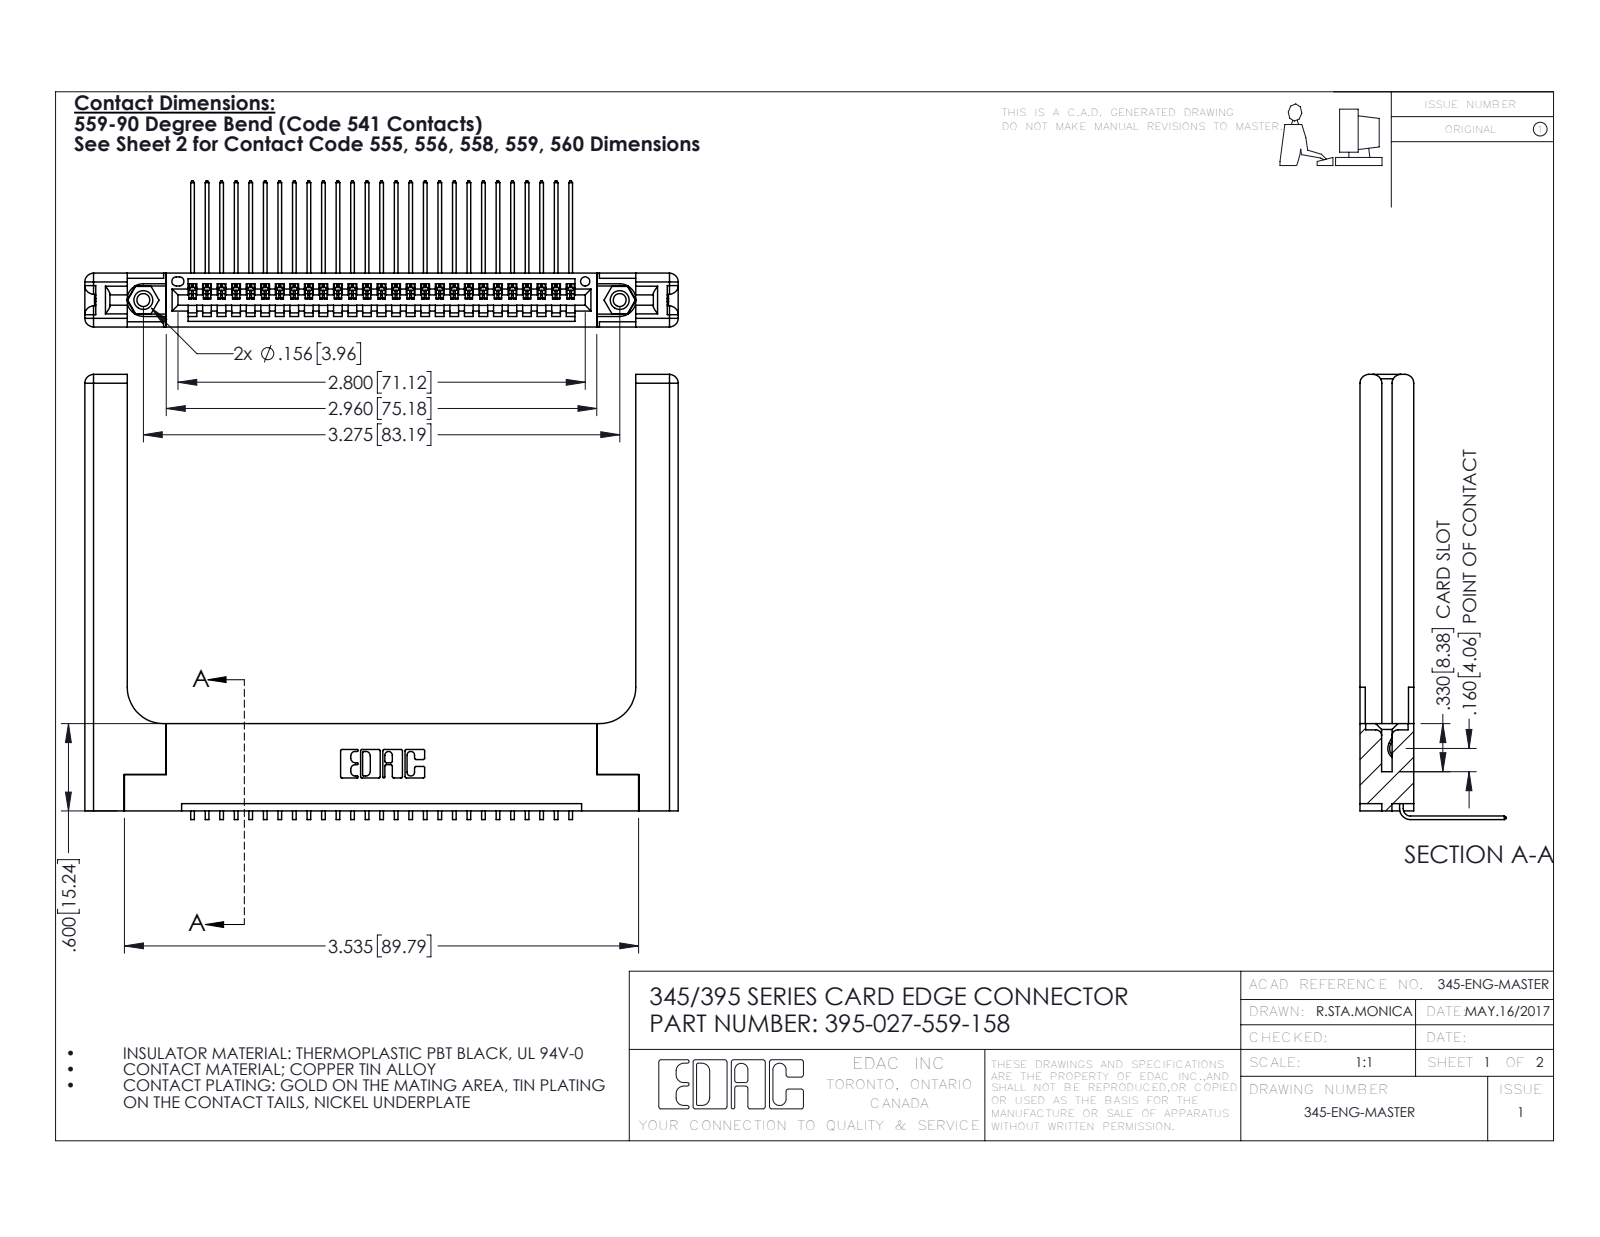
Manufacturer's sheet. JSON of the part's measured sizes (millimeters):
{"part_name": "345-220-058_345-220-058; 345-250-001_345-250-001-102; 345-292-001_558 559 Tail - 1; 395-027-559-158 (+1 more)", "step_written_by": "SolidWorks 2016 (CONFIG_CONTROL_DESIGN)", "units": "millimeters", "bodies": {"solids": 32, "faces": 2002, "planar": 1362, "cylindrical": 580, "other": 60}, "overall_size": [103.6, 77.7, 25.5], "volume_mm3": 18320, "surface_area_mm2": 18660, "round_holes": [[2.3, 2], [3.2, 2], [4, 2], [1.6, 1]], "round_bosses_or_shafts": [[3.9, 2]], "partial_cylinders_radius": [[0.2, 54], [0.3, 22], [1.5, 16], [0.2, 6], [0.8, 6], [0.7, 3], [0.8, 2], [0.8, 2]], "face_to_face_distances": [9.4, 1.8, 7.6, 5.1, 3.8, 3.8, 2, 2.5, 6.9, 0.6], "hole_center_spacings": [6.9, 77.2, 83.2]}
